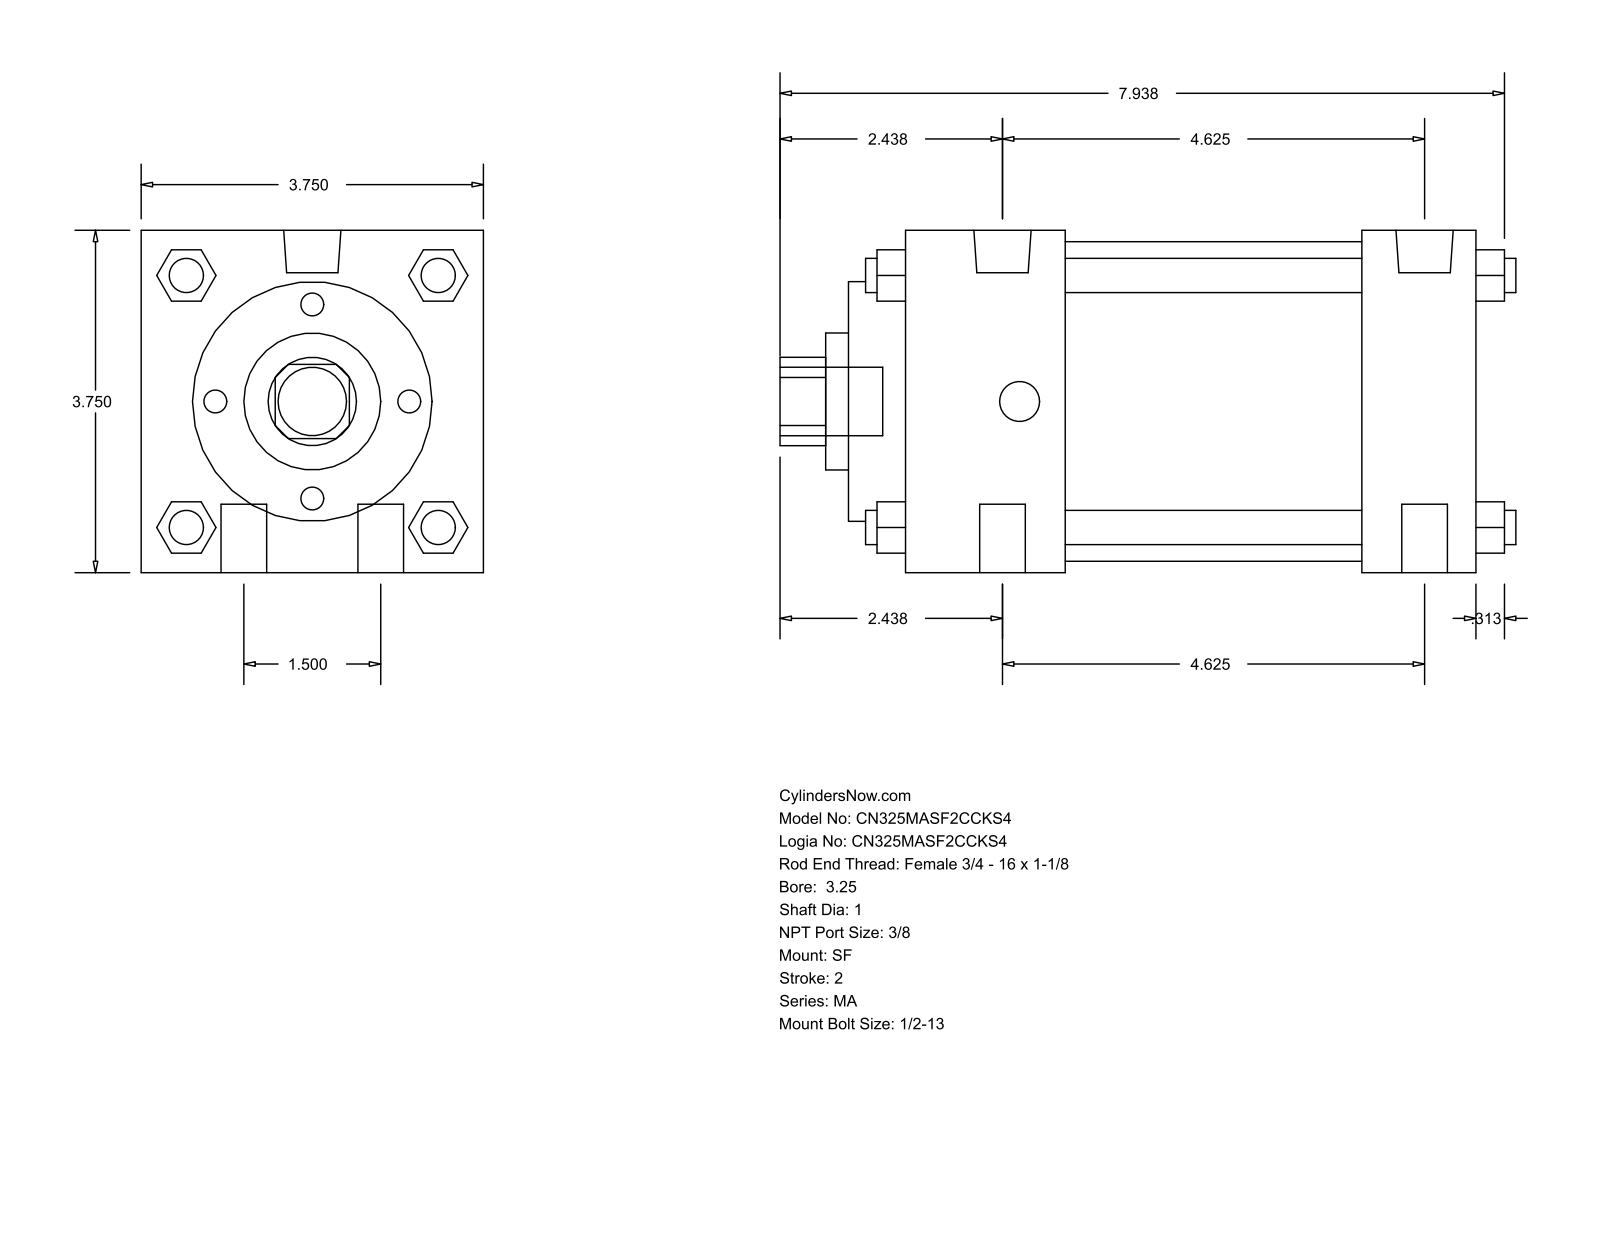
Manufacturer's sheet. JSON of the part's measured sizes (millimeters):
{"part_name": "MA_SF__0325_1", "step_written_by": "GSSL Pune (CONFIG_CONTROL_DESIGN)", "units": "millimeters", "bodies": {"solids": 0, "faces": 126, "planar": 95, "cylindrical": 31, "other": 0}, "overall_size": [204.79, 95.25, 95.25], "round_holes": [[25.4, 1], [38.1, 1], [66.67, 1], [88.9, 1]], "round_bosses_or_shafts": [[12.7, 4], [9.53, 4], [15.93, 2], [11.11, 2], [19.05, 1]], "partial_cylinders_radius": [[12.29, 1]], "face_to_face_distances": [95.24, 158.76, 15.87, 127.01, 31.75, 44.46, 82.55, 114.3, 60.33, 142.88]}
